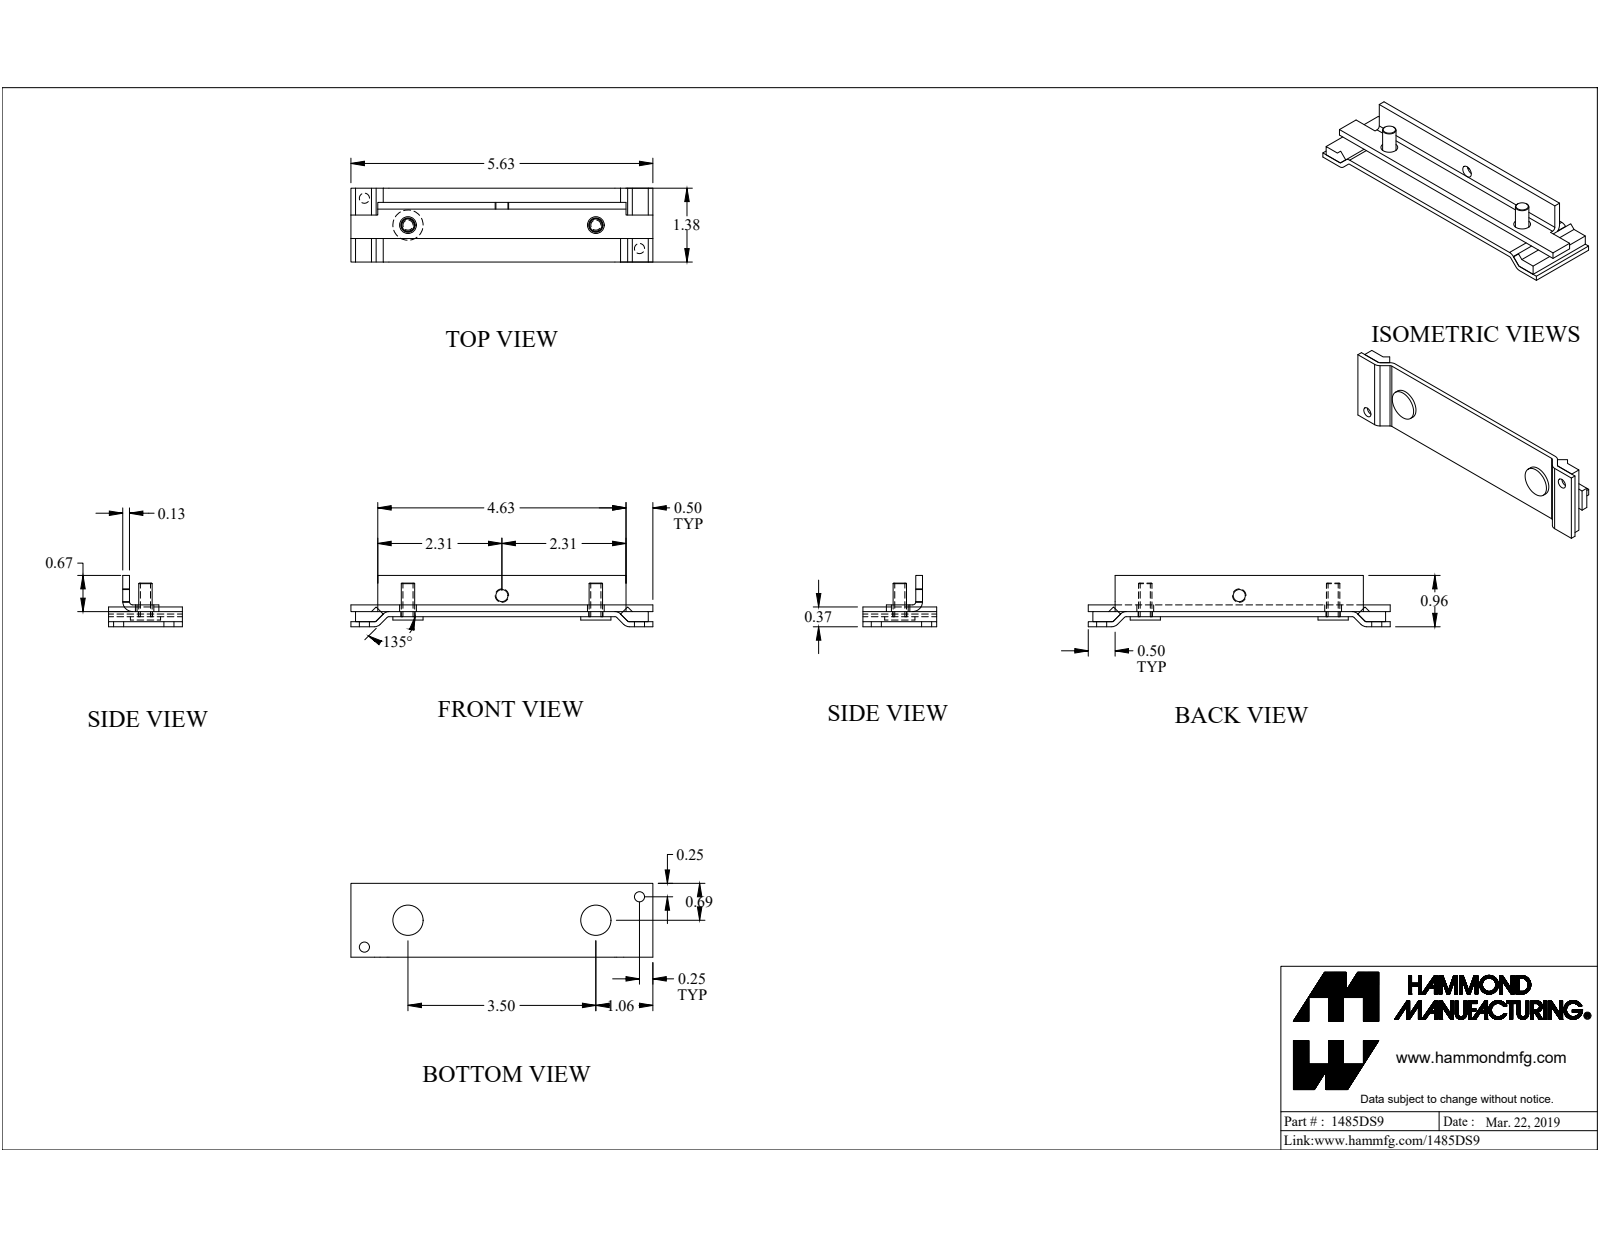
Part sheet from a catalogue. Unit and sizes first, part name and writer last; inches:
Units: inches
Overall size (bounding box): 5.625 × 1.375 × 0.956
Round holes (diameter × count): ⌀0.187 ×2, ⌀0.265 ×2, ⌀0.313 ×2, ⌀0.224 ×1
Round bosses / shafts (diameter × count): ⌀0.563 ×2, ⌀0.25 ×2
Partial cylindrical surfaces — rounded edges, fillets, slot ends (radius × count): R0.048 ×4, R0.143 ×4, R0.06 ×1, R0.185 ×1
Main face-to-face distances: 0.095, 0.125, 0.22, 0.093, 0.188, 0.313, 0.095, 0.187, 0.283, 0.673
Hole centre spacings: 0.923, 0.954, 3.5, 4.335, 4.341, 5.21
Volume: 1.792 in³ · Surface area: 36.8 in²
Bodies: 6 solids, 71 faces (48 planar, 21 cylindrical, 2 other)
Part name (STEP PRODUCT): 1485DS9
STEP written by: SolidWorks 2019 (CONFIG_CONTROL_DESIGN)
